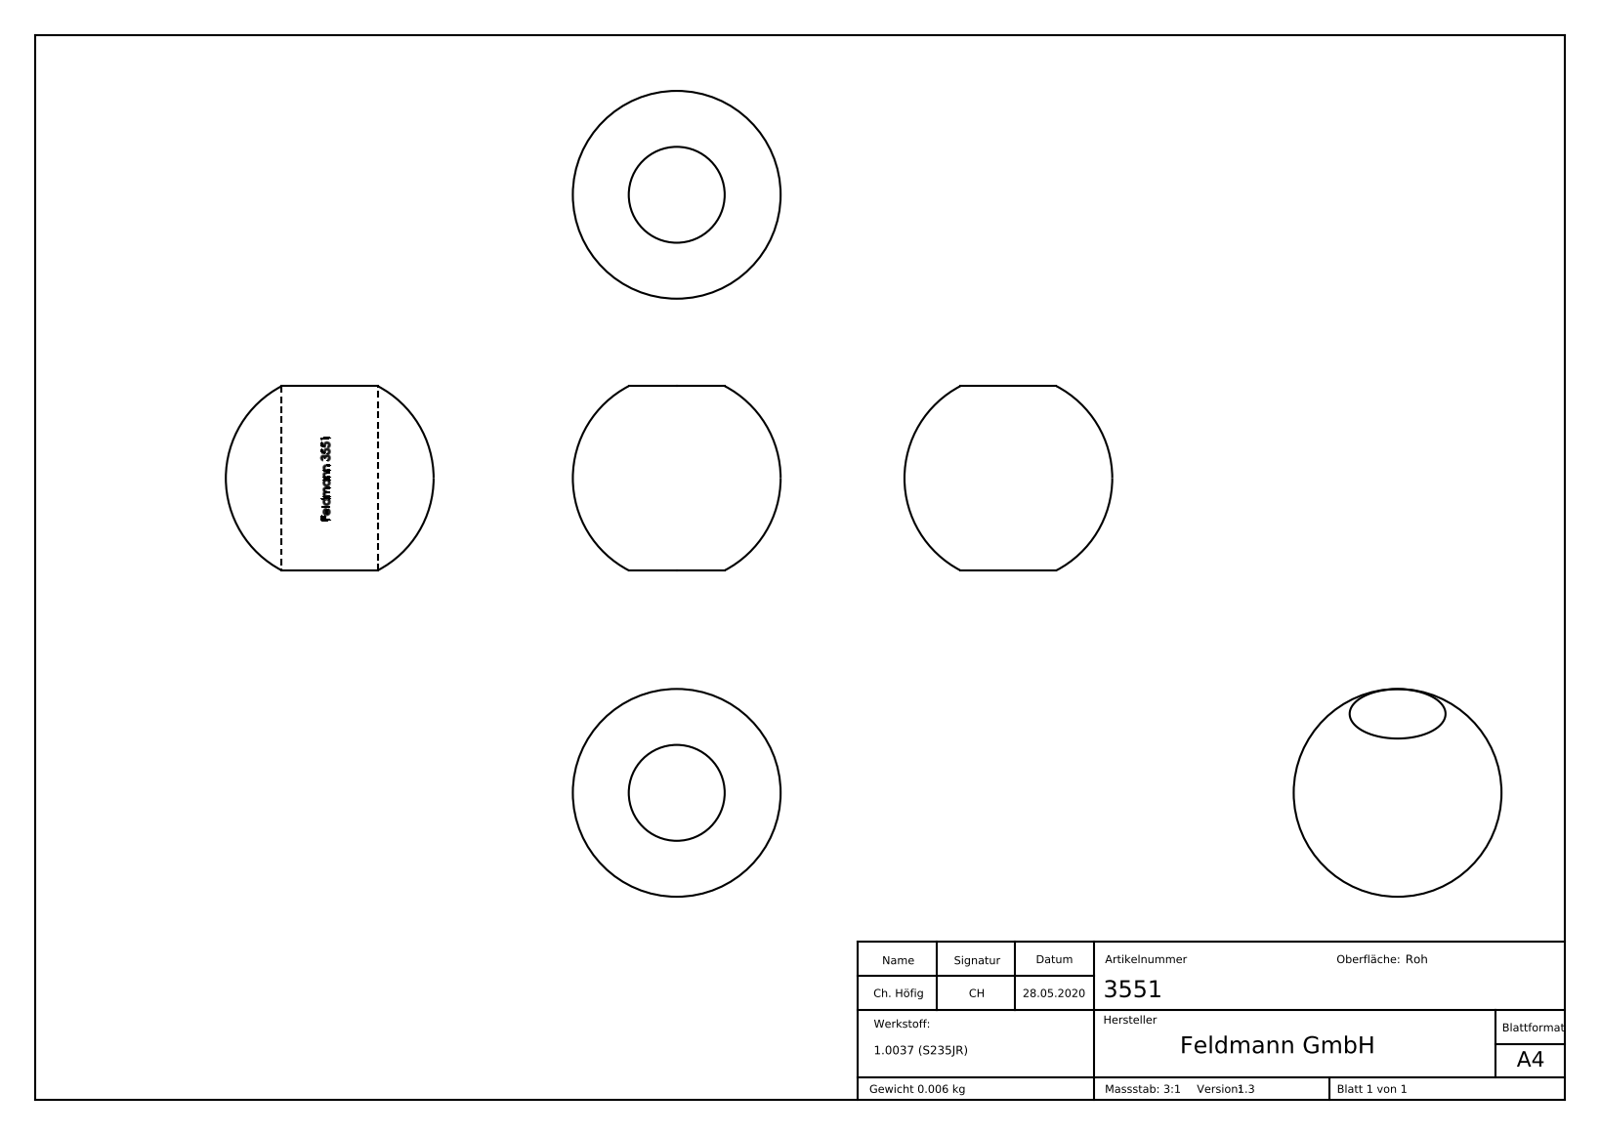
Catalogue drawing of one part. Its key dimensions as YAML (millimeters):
part_name: "3551"
step_written_by: "SolidWorks 2015 (CONFIG_CONTROL_DESIGN)"
units: millimeters
bodies: {solids: 1, faces: 170, planar: 75, cylindrical: 16, other: 79}
overall_size: [13, 13, 11.53]
volume: 803
surface_area: 691
round_holes:
  - {diameter: 6, count: 1}
partial_cylinders:
  - {radius: 3.1, count: 1}
face_to_face_distances: [0.45, 0.55, 0.5, 4.29, 0.53, 0.81, 5.1, 1.79, 3.79, 1.84]
